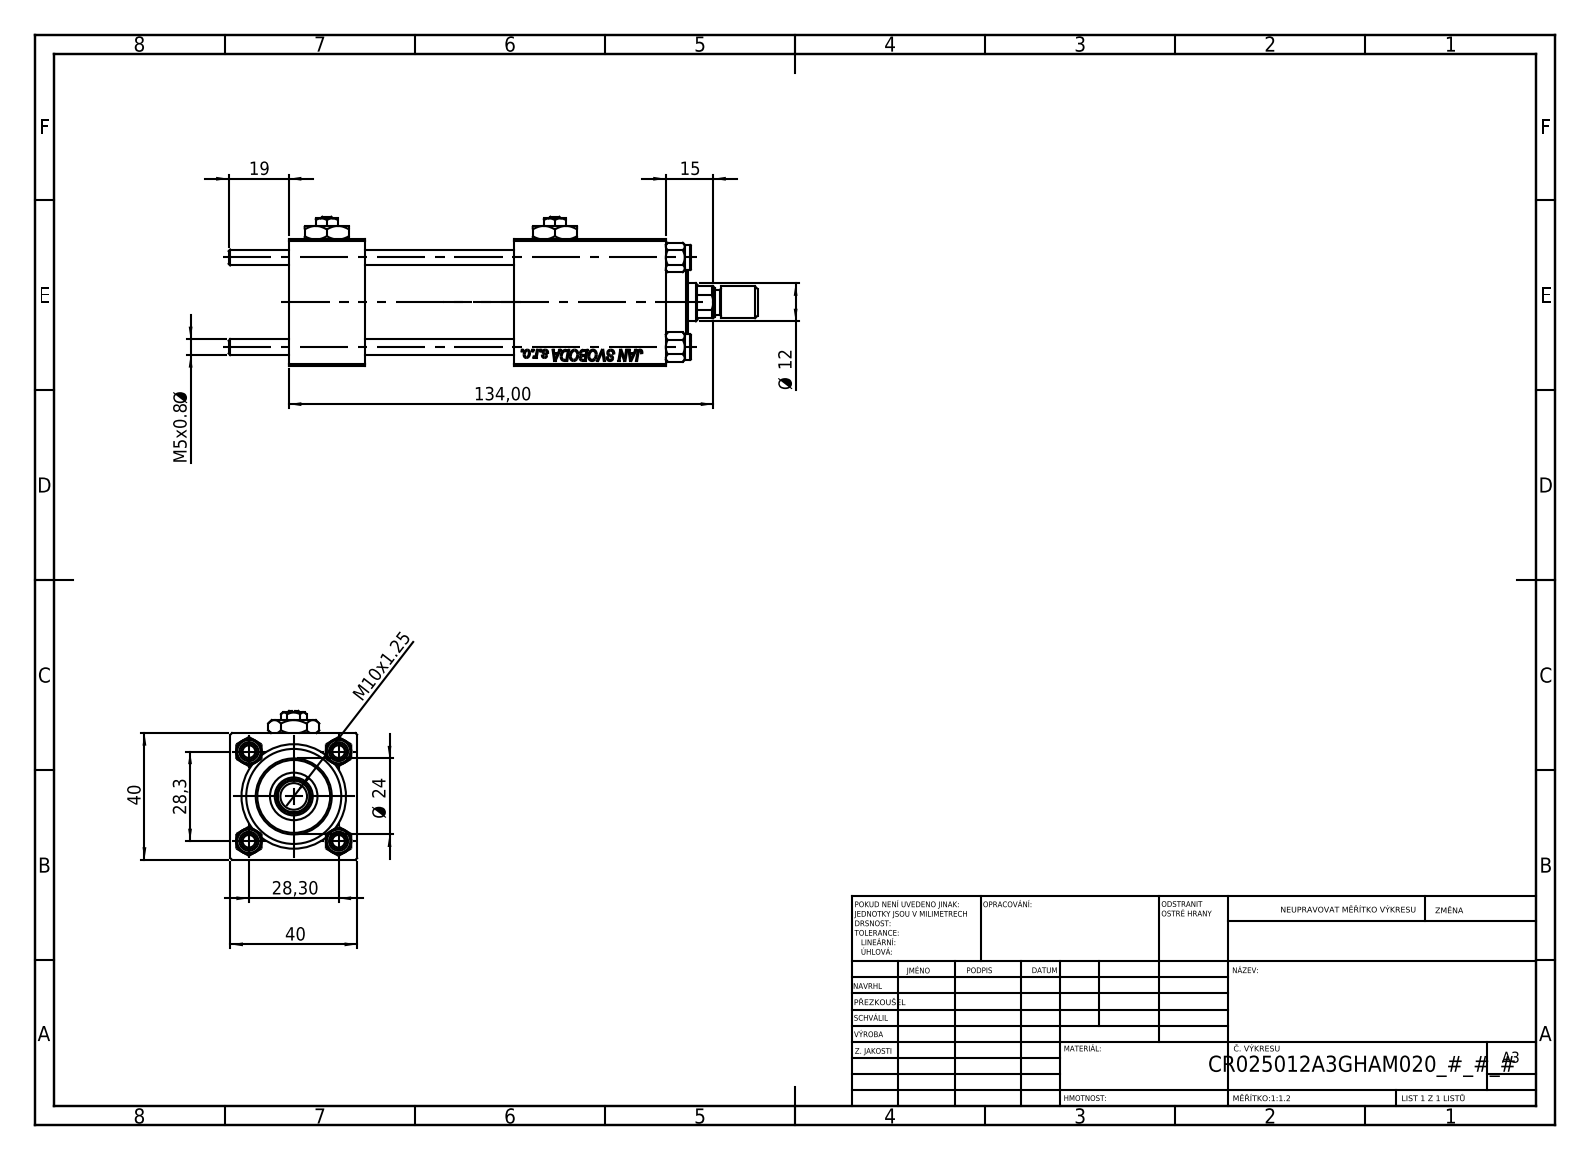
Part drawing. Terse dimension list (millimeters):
name: ROD_END_AH; V215CR_BODY_A; V215CR_VCP; V215_VC_A (+3 more)
written by: SolidWorks 2019 (CONFIG_CONTROL_DESIGN)
unit: mm
bodies: 14 solids, 1246 faces (568 planar, 94 cylindrical, 584 other)
size: 167 × 47 × 40
volume: 144 451 mm³; area: 61 250 mm²
holes: 4× ⌀5, 3× ⌀20, 2× ⌀7, 2× ⌀13.16, 1× ⌀6.5, 1× ⌀12, 1× ⌀15, 1× ⌀25, 1× ⌀30
bosses: 5× ⌀8, 1× ⌀31, 1× ⌀24, 1× ⌀10
rounds: 1× R5.5
face distances: 40, 24, 39.8, 119, 95, 90.3, 66.3, 28.7, 71, 47
hole spacings: 20.01, 28.3, 40.02, 72
